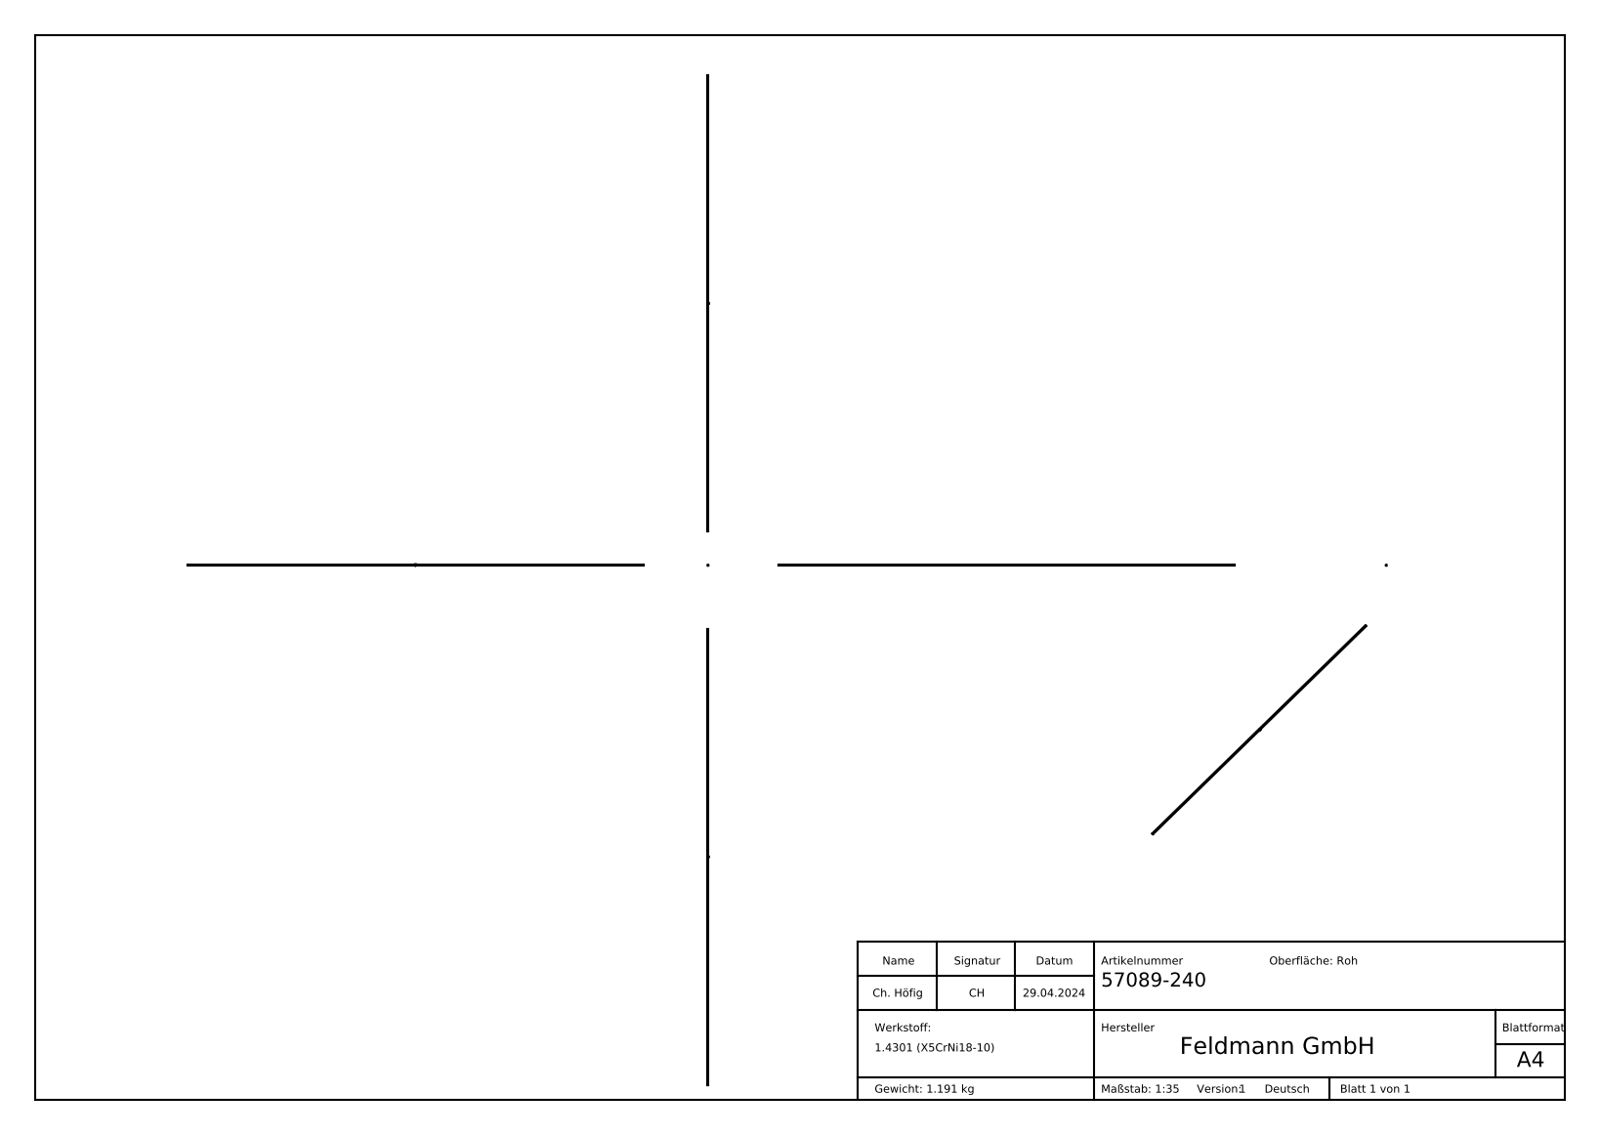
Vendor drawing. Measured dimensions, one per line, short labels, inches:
name: 57089-240
written by: SolidWorks 2018 (CONFIG_CONTROL_DESIGN)
unit: in
bodies: 1 solid, 278 faces (105 planar, 34 cylindrical, 139 other)
size: 118.11 × 0.315 × 0.315
volume: 9.202 in³; area: 117 in²
bosses: 1× ⌀0.315
rounds: 1× R0.154
face distances: 118.11, 0.048, 0.08, 0.125, 0.095, 0.03, 0.044, 0.05, 0.033, 0.076
